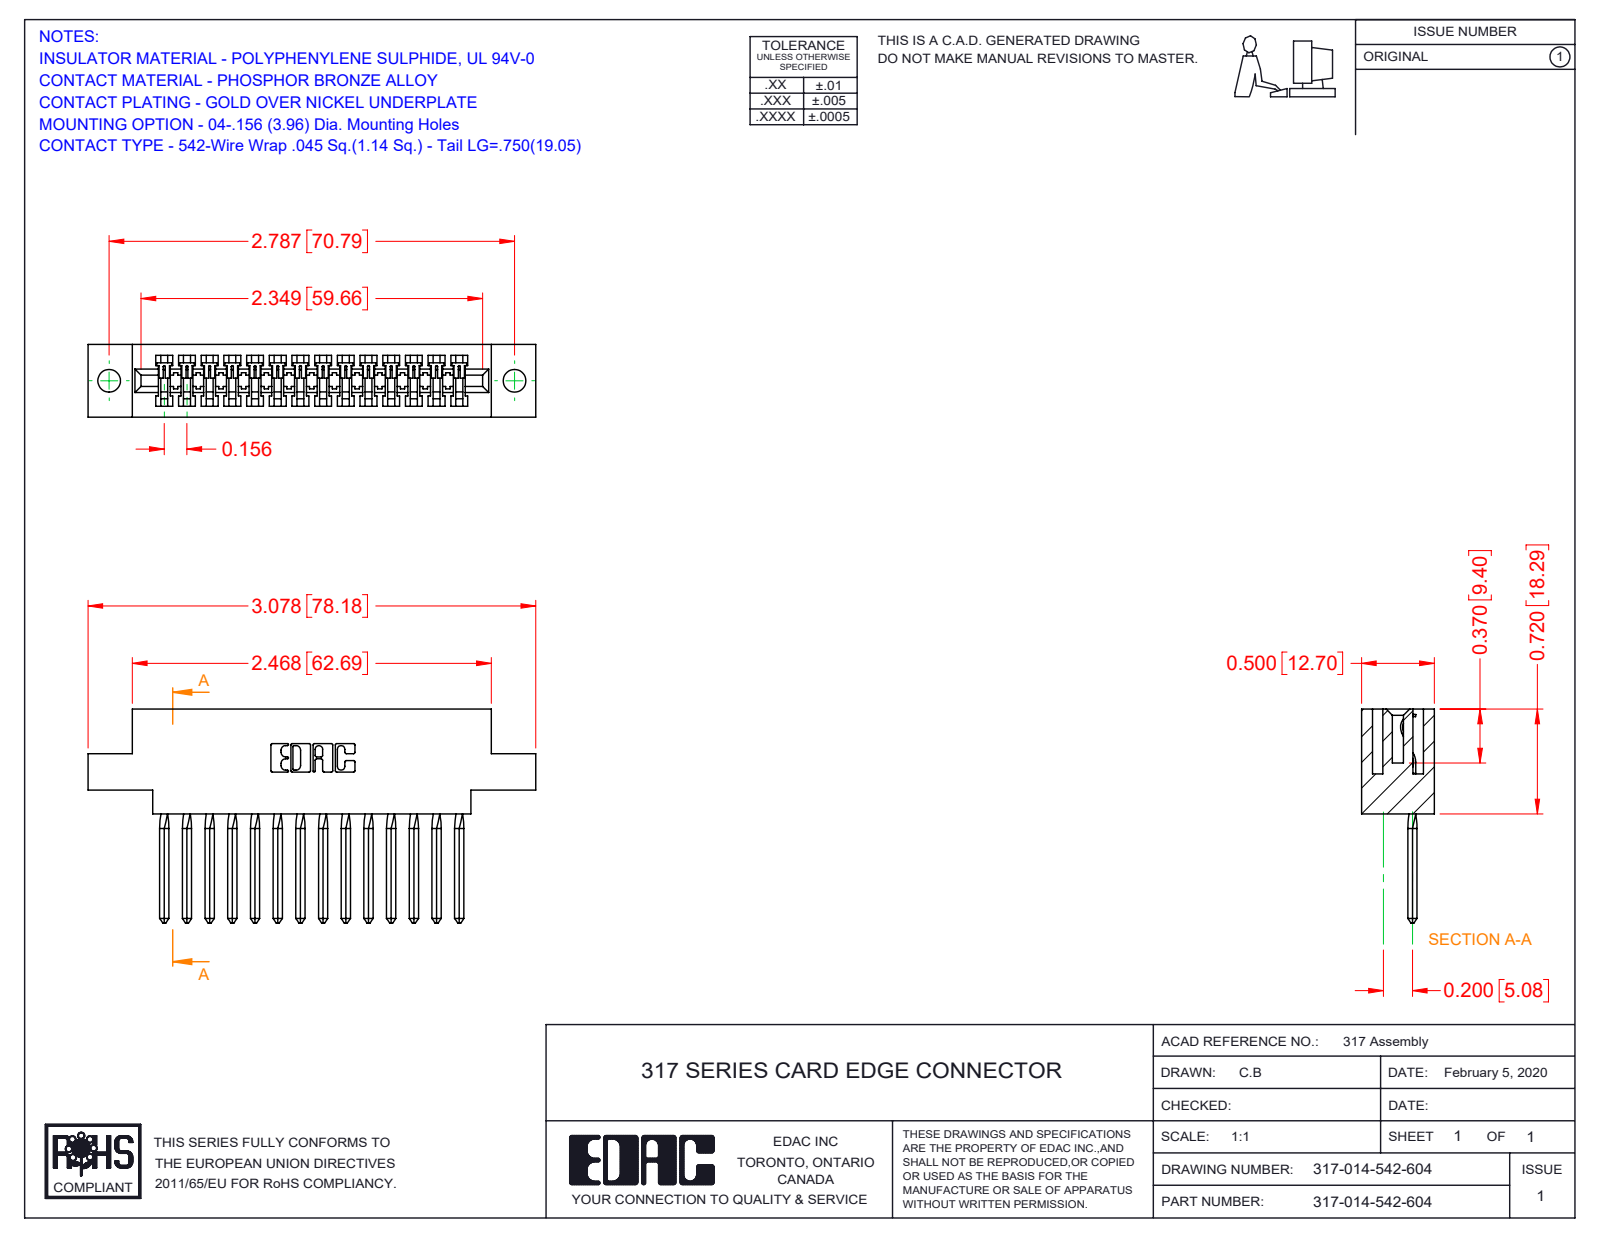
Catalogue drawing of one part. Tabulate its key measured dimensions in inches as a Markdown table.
| quantity | value |
| --- | --- |
| part name | 317-014-542-604; 317 Part_.156 Dia - TH; 317-290-003_542 |
| STEP written by | SolidWorks 2016 (CONFIG_CONTROL_DESIGN) |
| units | inches |
| bodies | 15 solids, 1152 faces (954 planar, 142 cylindrical, 56 other) |
| overall size | 3.078 × 1.47 × 0.5 |
| volume | 0.686 in³ |
| surface area | 19.98 in² |
| round holes (diameter × count) | 0.156 × 2 |
| partial cylindrical surfaces (radius × count) | 0.006 × 28, 0.01 × 22, 0.007 × 6, 0.031 × 6, 0.026 × 3, 0.074 × 1, 0.089 × 1, 0.1 × 1 |
| main face-to-face distances | 0.5, 0.075, 0.425, 0.11, 0.35, 0.065, 0.22, 0.136, 0.72, 0.116 |
| hole center spacings | 2.787 |
